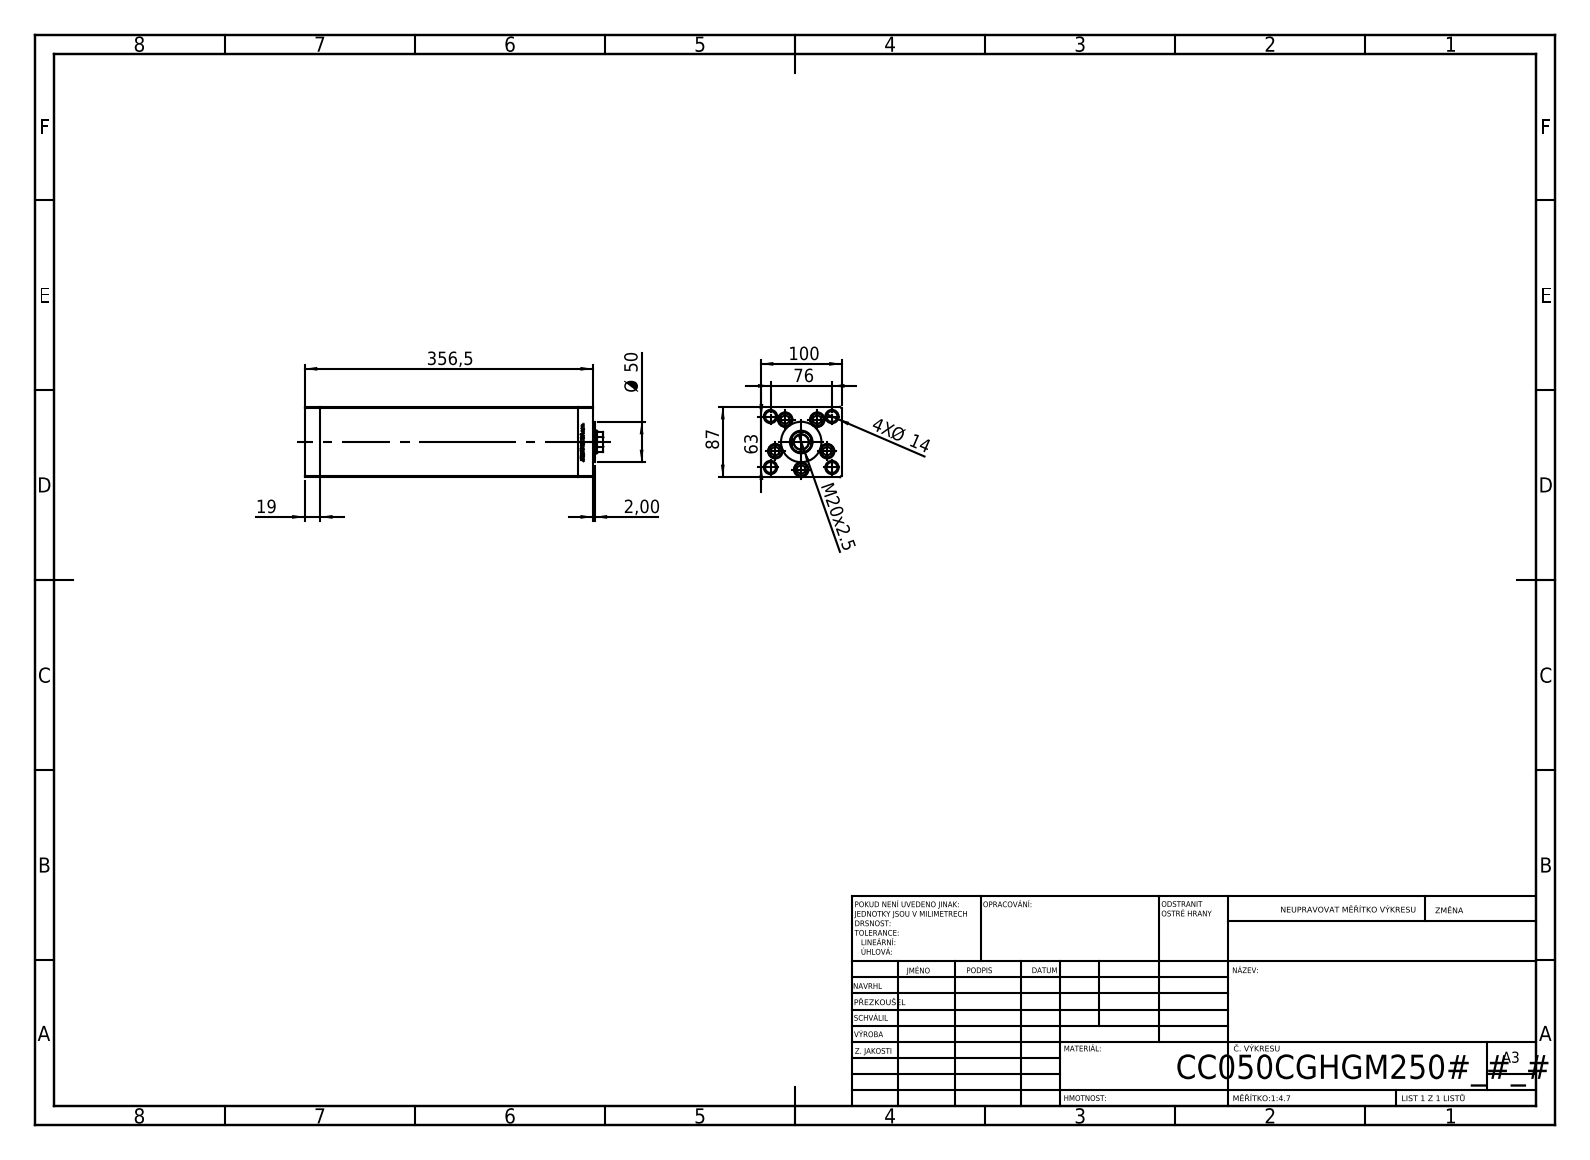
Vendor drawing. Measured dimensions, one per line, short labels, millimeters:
name: V220C_VC_C; V220C BACK_C; ALLEN BOLT; V220C_C MIDDLE (+1 more)
written by: SolidWorks 2019 (CONFIG_CONTROL_DESIGN)
unit: mm
bodies: 13 solids, 1186 faces (548 planar, 176 cylindrical, 462 other)
size: 369.5 × 100 × 87
volume: 2 535 000 mm³; area: 343 339 mm²
holes: 9× ⌀13.5, 5× ⌀18, 4× ⌀2, 4× ⌀12, 4× ⌀13.16, 4× ⌀16.5, 1× ⌀17, 1× ⌀18.5, 1× ⌀28
bosses: 5× ⌀8, 4× ⌀17, 1× ⌀50
rounds: 2× R0.93, 1× R13.5
face distances: 100, 87, 19, 318.5, 337.5, 34.25, 356.5, 76.5, 10.5, 4
hole spacings: 34, 49.36, 18.59, 21.03, 38.08, 39.27, 40.83, 43.24
